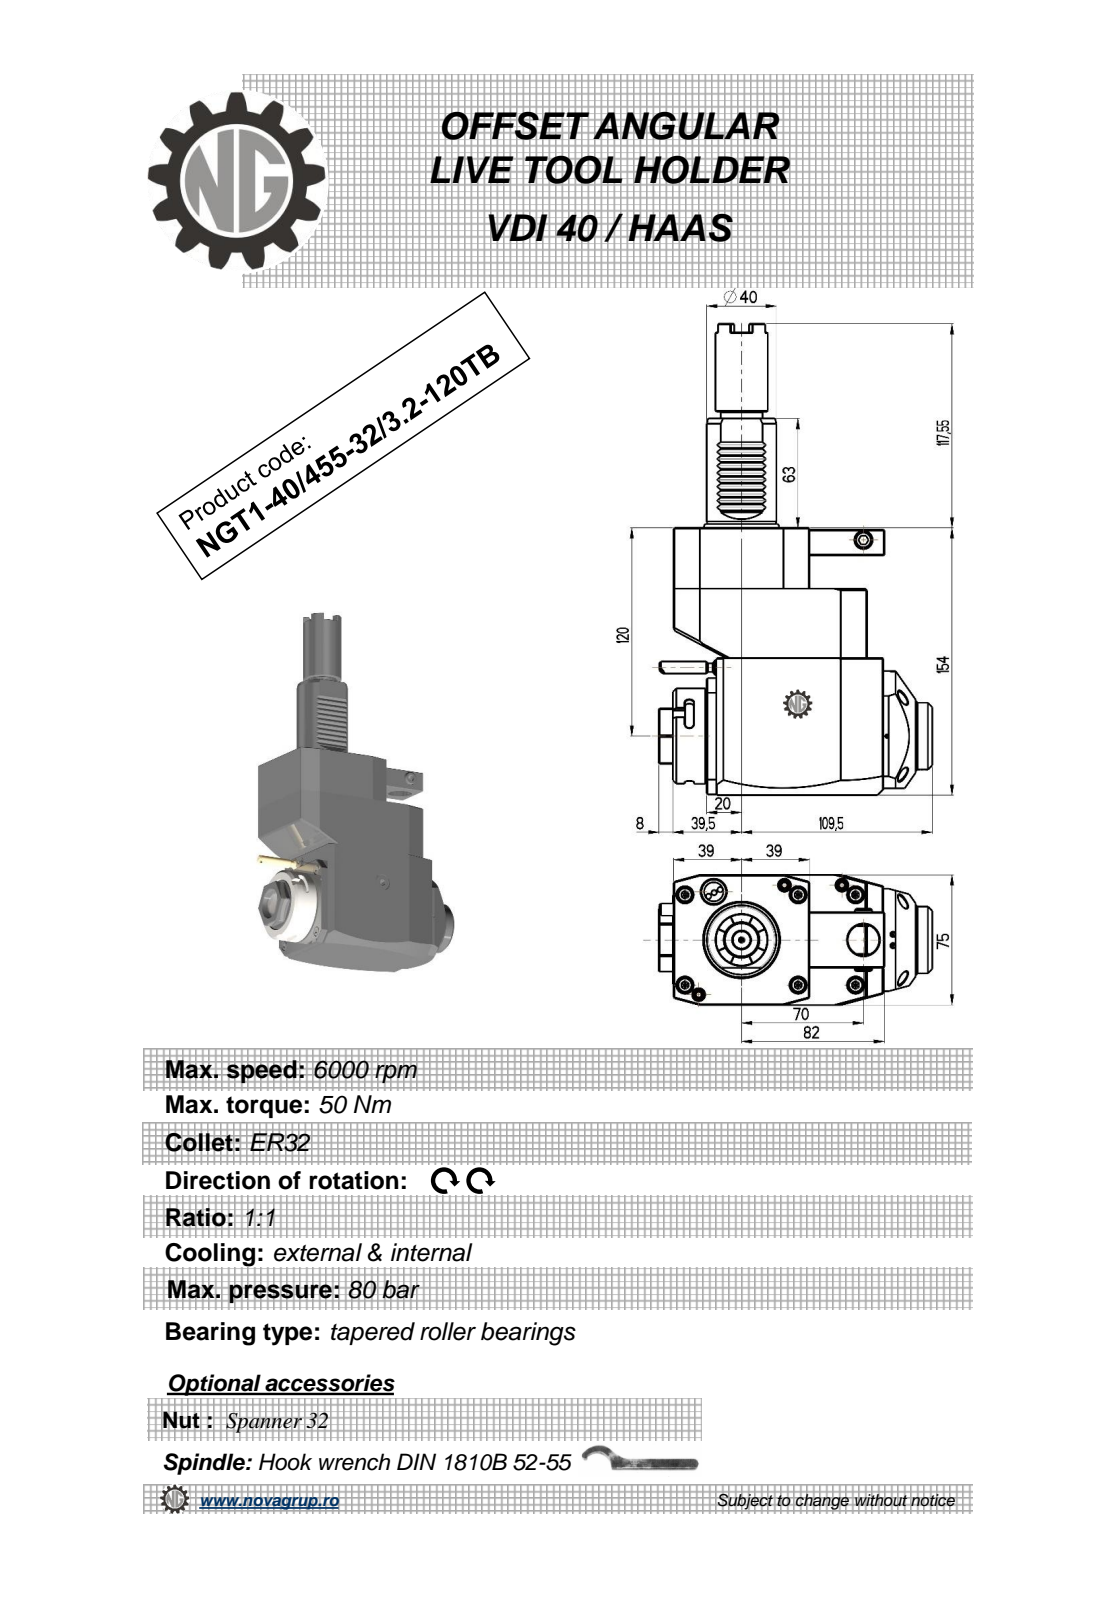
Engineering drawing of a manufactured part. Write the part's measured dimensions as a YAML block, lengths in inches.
part_name: "NGT1_40_455_32_3_2_120TB"
step_written_by: "PRO/ENGINEER BY PARAMETRIC TECHNOLOGY CORPORATION, 2010280 (CONFIG_CONTROL_DESIGN)"
units: inches
bodies: {solids: 1, faces: 380, planar: 222, cylindrical: 72, other: 86}
overall_size: [10.691, 6.181, 2.953]
volume: 80.92
surface_area: 150.4
round_holes:
  - {diameter: 0.098, count: 1}
  - {diameter: 0.118, count: 1}
  - {diameter: 0.374, count: 1}
  - {diameter: 0.709, count: 1}
  - {diameter: 0.787, count: 1}
  - {diameter: 0.906, count: 1}
round_bosses_or_shafts:
  - {diameter: 0.353, count: 2}
  - {diameter: 2.165, count: 1}
  - {diameter: 1.89, count: 1}
  - {diameter: 1.575, count: 1}
  - {diameter: 1.516, count: 1}
  - {diameter: 1.181, count: 1}
  - {diameter: 0.945, count: 1}
  - {diameter: 0.394, count: 1}
partial_cylinders:
  - {radius: 0.012, count: 10}
  - {radius: 0.098, count: 6}
  - {radius: 7.087, count: 2}
  - {radius: 0.02, count: 1}
  - {radius: 0.167, count: 1}
  - {radius: 0.965, count: 1}
  - {radius: 1.476, count: 1}
face_to_face_distances: [2.953, 6.063, 0.748, 2.323, 0.02, 4.37, 3.622, 1.378, 4.685, 2.106]
hole_center_spacings: [1.701, 2.756, 2.956, 4.429]
